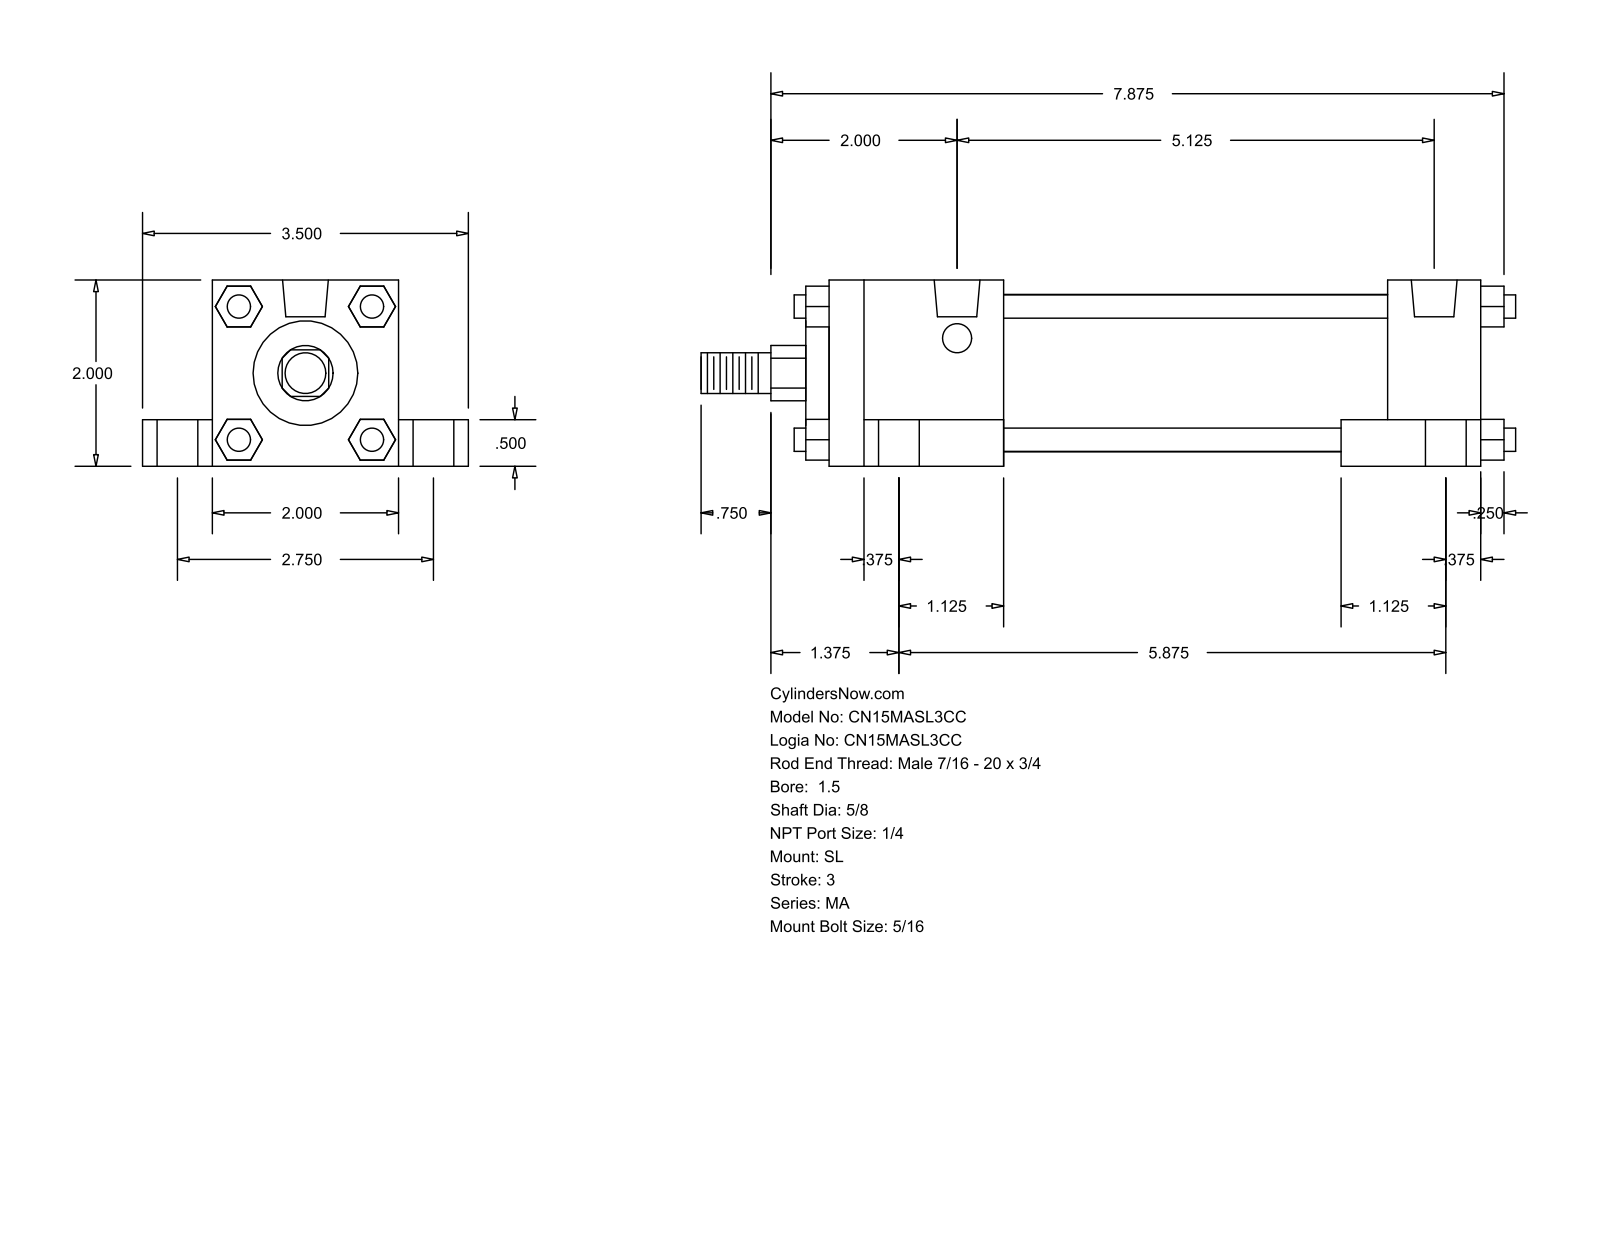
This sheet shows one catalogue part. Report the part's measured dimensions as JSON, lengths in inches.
{"part_name": "MA_SL__0150_0.625", "step_written_by": "GSSL Pune (CONFIG_CONTROL_DESIGN)", "units": "inches", "bodies": {"solids": 0, "faces": 148, "planar": 112, "cylindrical": 36, "other": 0}, "overall_size": [8.75, 3.5, 2], "round_holes": [[0.313, 4], [0.437, 4], [0.687, 4], [0.492, 2]], "round_bosses_or_shafts": [[0.25, 4], [1.69, 1], [1.125, 1], [0.625, 1], [0.437, 1]], "partial_cylinders_radius": [[0.297, 1]], "face_to_face_distances": [2, 0.75, 1.5, 7, 2.75, 0.5, 0.375, 1, 0.25, 7.25], "hole_center_spacings": [1.38, 1.51, 2.75, 5.125, 5.427, 5.875, 5.912, 6.487]}
